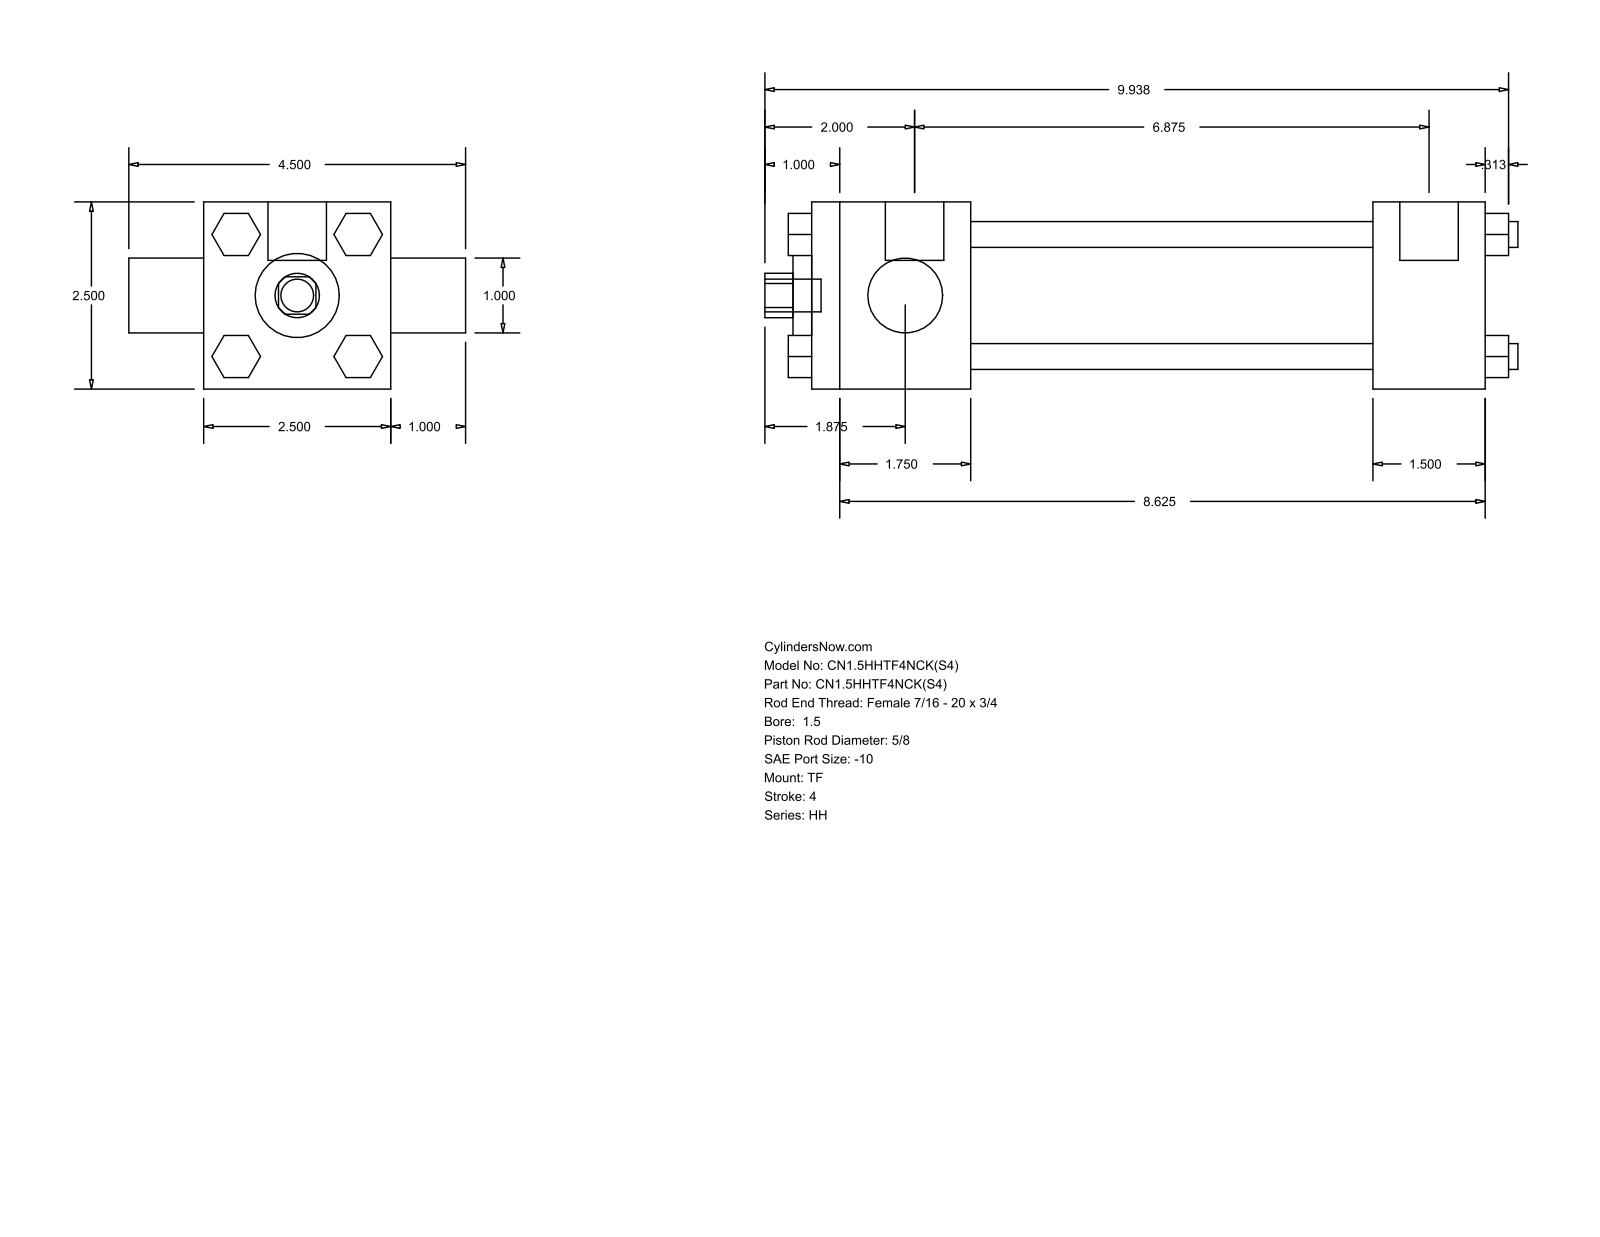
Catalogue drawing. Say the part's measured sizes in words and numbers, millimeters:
The part is named "HH_TF__0150_0.625". Its 3-D file was written by "GSSL Pune (CONFIG_CONTROL_DESIGN)". It is 0 solids with 120 faces: 92 planar, 28 cylindrical and 0 other. Overall it measures 255.59 by 114.3 by 63.5 millimeters. Round holes: 1 of diameter 15.88, 1 of diameter 25.4, 1 of diameter 28.57, 1 of diameter 44.45. Round bosses or shafts: 4 of diameter 8.76, 3 of diameter 5.56, 2 of diameter 19.84, 1 of diameter 11.11. Partial cylindrical surfaces (rounded edges, fillets, slot ends): 1 of radius 7.54. The main face-to-face distances are 63.5, 228.59, 53.97, 174.62, 190.5, 136.53, 38.09, 25.4, 20.7, 14.29.
